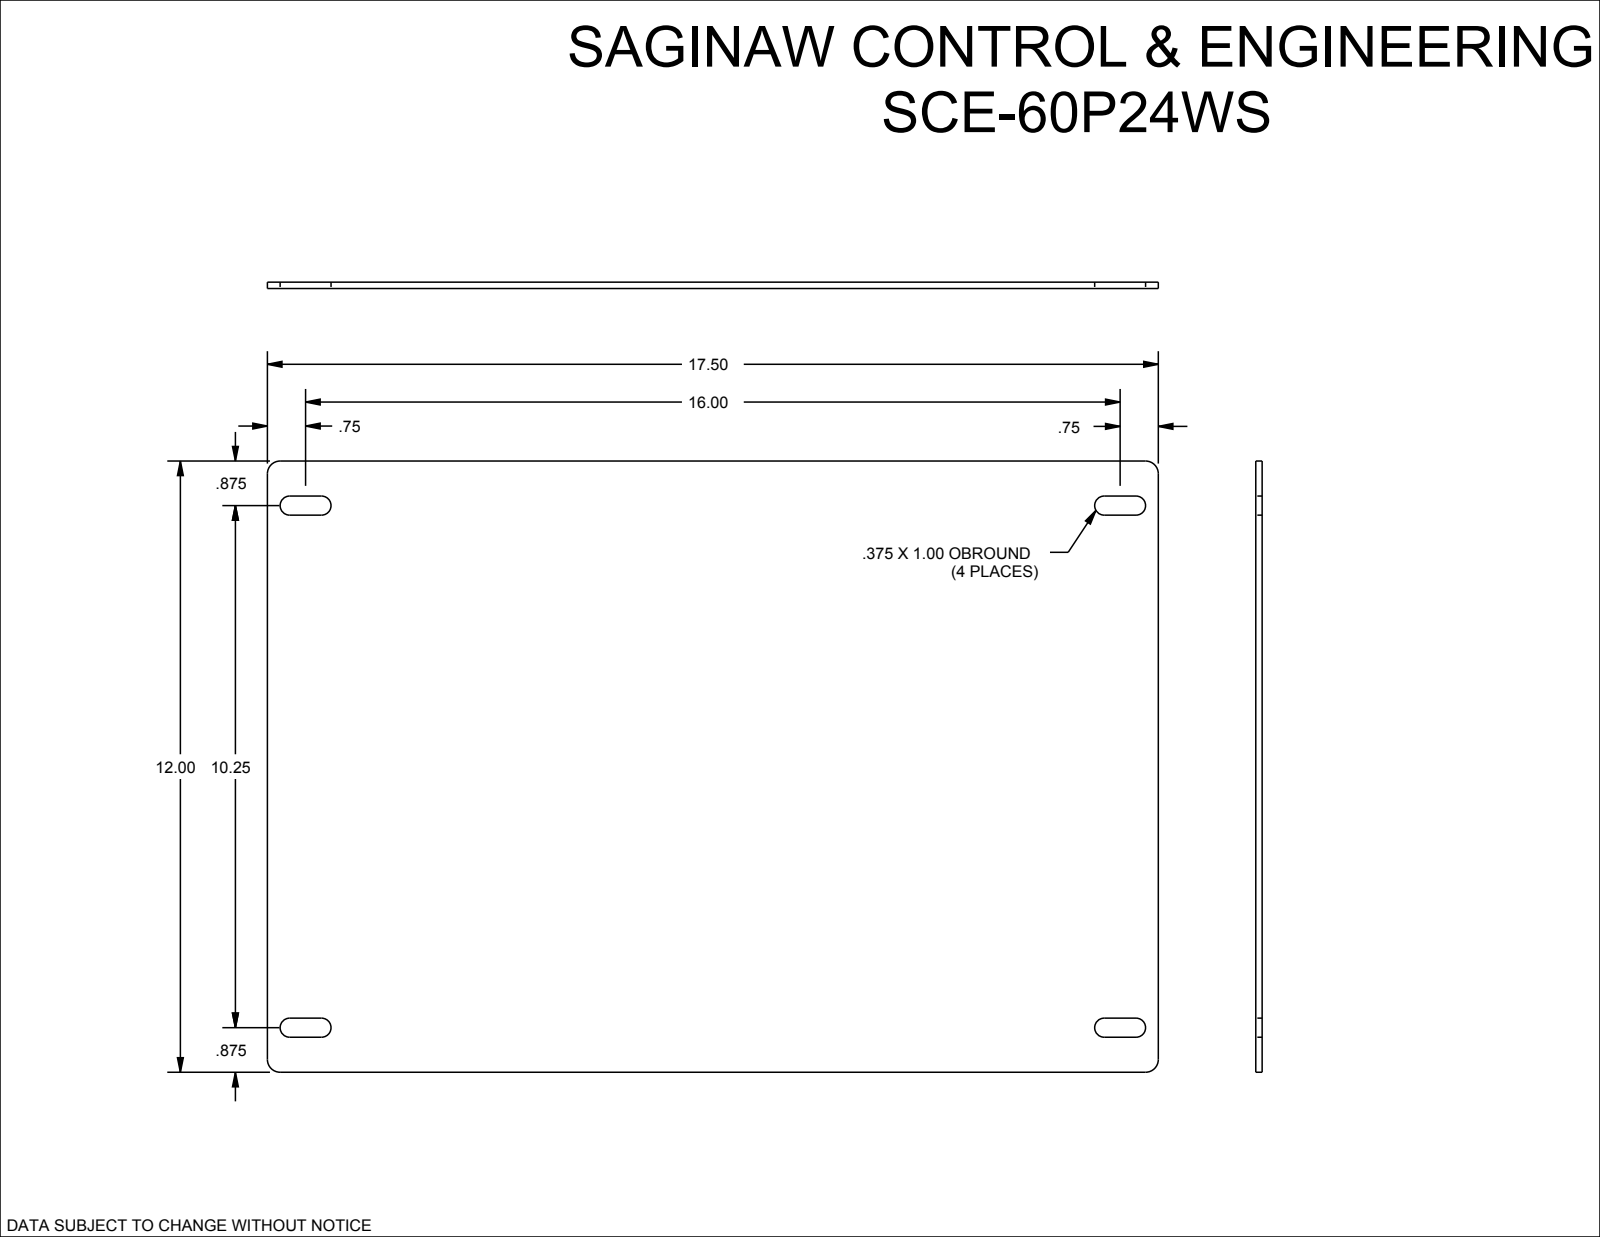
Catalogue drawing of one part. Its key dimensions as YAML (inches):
part_name: "SCE-60P24WS"
step_written_by: "SolidWorks 2019 (CONFIG_CONTROL_DESIGN)"
units: inches
bodies: {solids: 1, faces: 26, planar: 14, cylindrical: 12, other: 0}
overall_size: [17.5, 12, 0.125]
volume: 26.07
surface_area: 425.7
partial_cylinders:
  - {radius: 0.187, count: 4}
  - {radius: 0.188, count: 4}
  - {radius: 0.25, count: 4}
face_to_face_distances: [0.125, 12, 17.5, 0.687, 1.063, 10.937, 11.313, 0.375, 10.25, 10.625]
